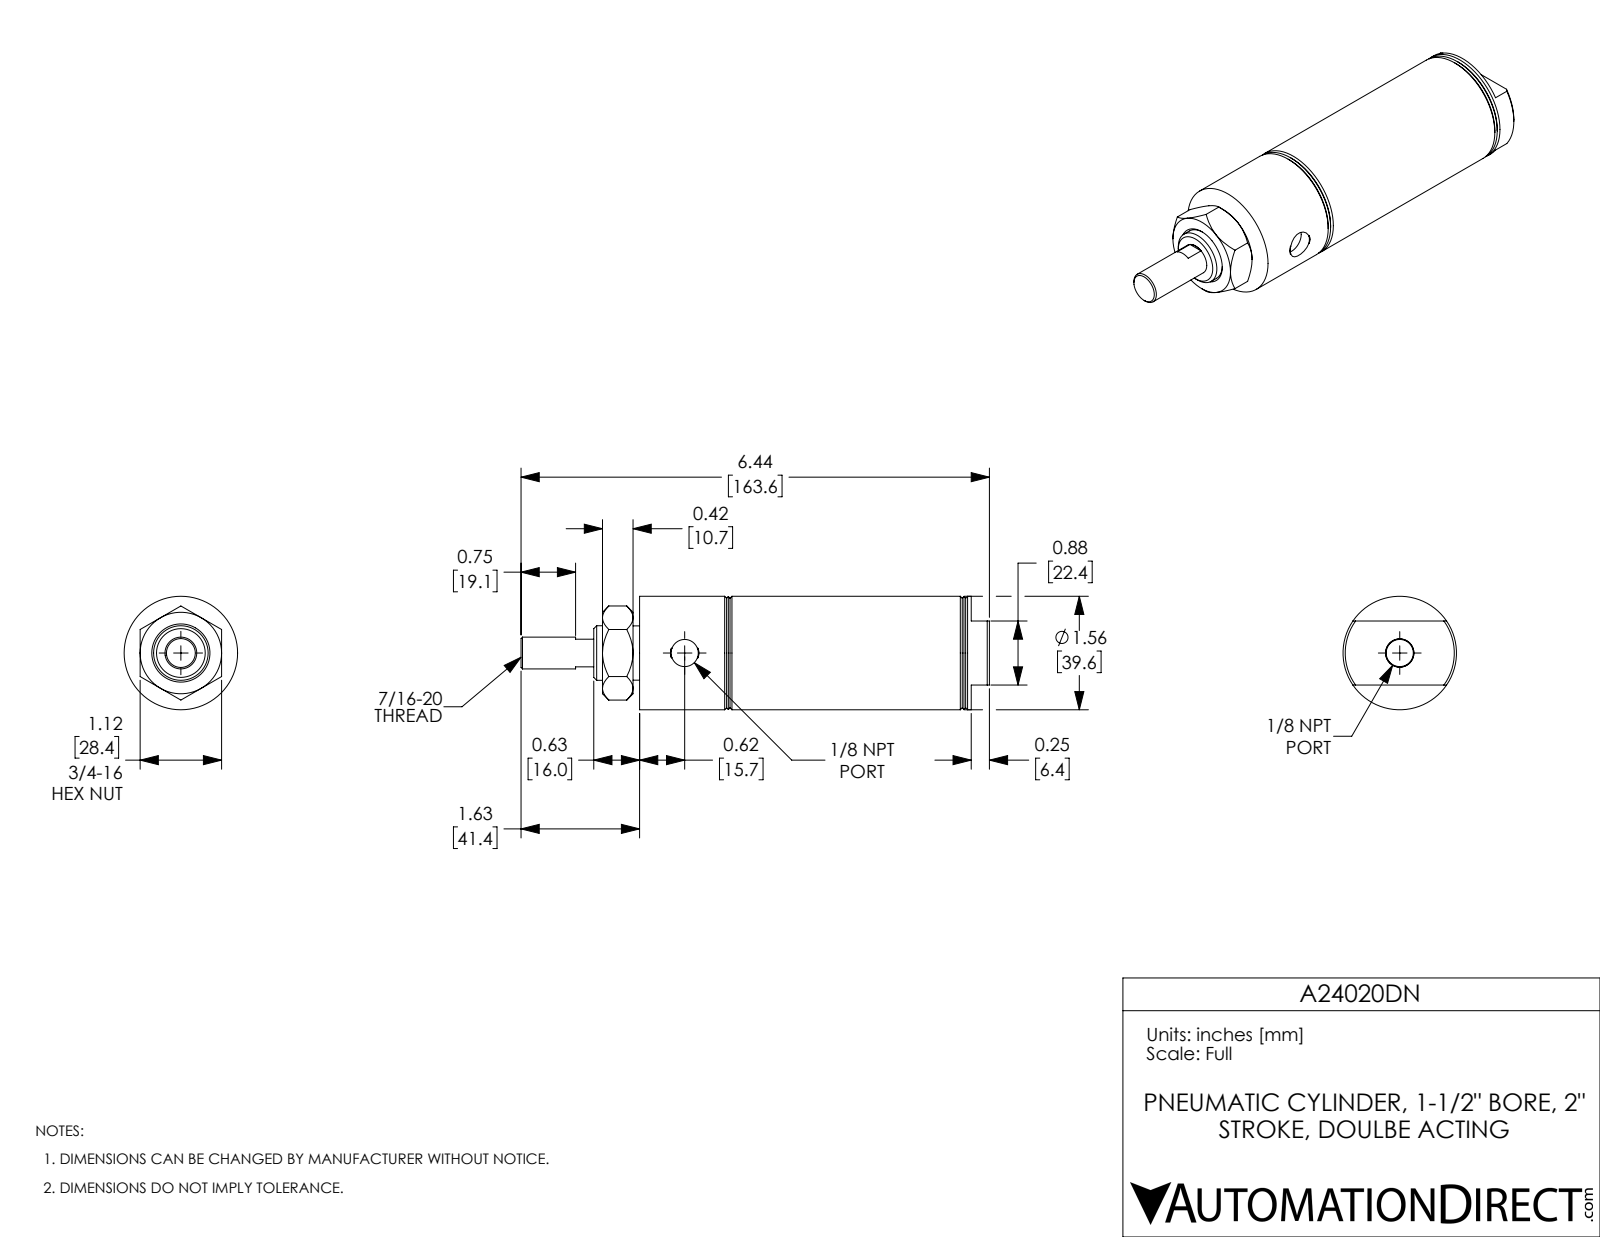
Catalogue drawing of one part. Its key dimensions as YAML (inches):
part_name: "A24020DN-MainBody; A24020DN; A24020DN_Mounting Nut_D-3556; A24020DN-Rod"
step_written_by: "SolidWorks 2017 (AUTOMOTIVE_DESIGN)"
units: inches
bodies: {solids: 3, faces: 104, planar: 32, cylindrical: 24, other: 48}
overall_size: [6.44, 1.56, 1.56]
volume: 6.436
surface_area: 63.6
round_holes:
  - {diameter: 0.374, count: 2}
  - {diameter: 0.437, count: 1}
  - {diameter: 0.75, count: 1}
  - {diameter: 1.5, count: 1}
round_bosses_or_shafts:
  - {diameter: 1.56, count: 1}
  - {diameter: 0.746, count: 1}
face_to_face_distances: [2.5, 0.5, 2, 3.84, 3.34, 1.34, 0.97, 1.47, 3.47, 4.81]
